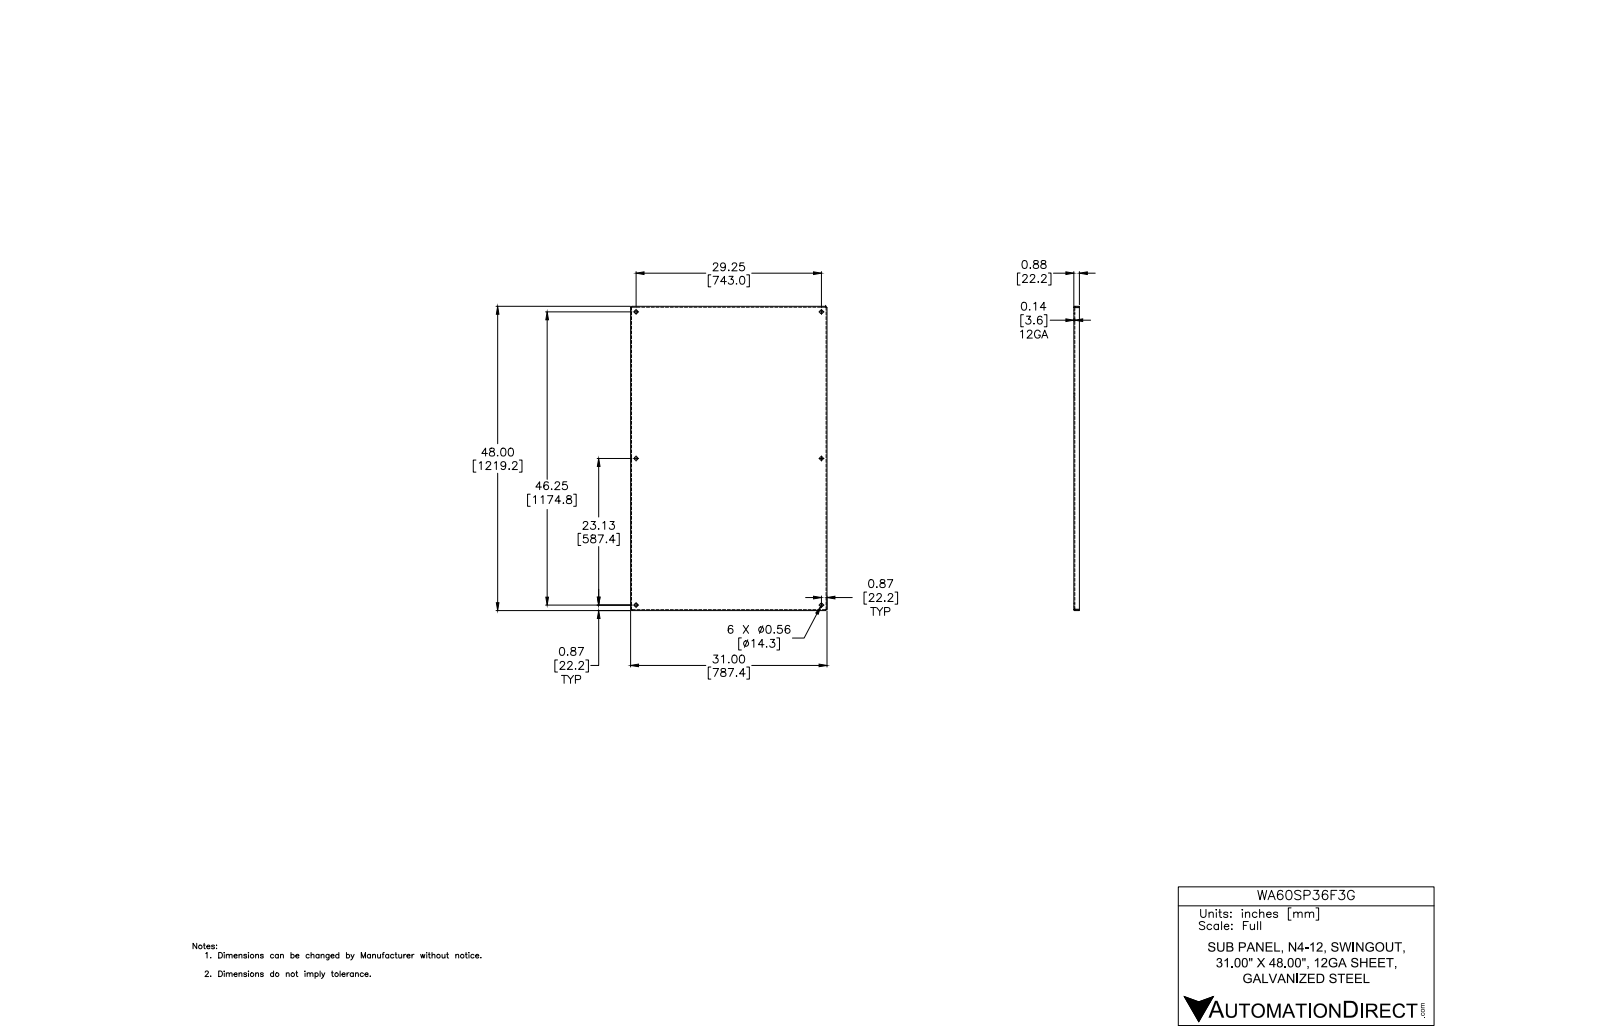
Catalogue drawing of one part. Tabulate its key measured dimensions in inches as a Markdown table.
| quantity | value |
| --- | --- |
| part name | WA60SP24F3G-WA90SP36F4G |
| STEP written by | Autodesk Inventor 2012 (AUTOMOTIVE_DESIGN) |
| units | inches |
| bodies | 1 solid, 42 faces (22 planar, 12 cylindrical, 8 other) |
| overall size | 48 × 31 × 0.875 |
| volume | 150.4 in³ |
| surface area | 3 224 in² |
| round holes (diameter × count) | 0.563 × 4 |
| partial cylindrical surfaces (radius × count) | 0.031 × 4, 0.125 × 4 |
| main face-to-face distances | 0.094, 30.906, 47.906, 31, 30.813, 47.813, 48, 0.781, 0.875, 0.16 |
| hole center spacings | 29.25, 46.25, 54.723 |
